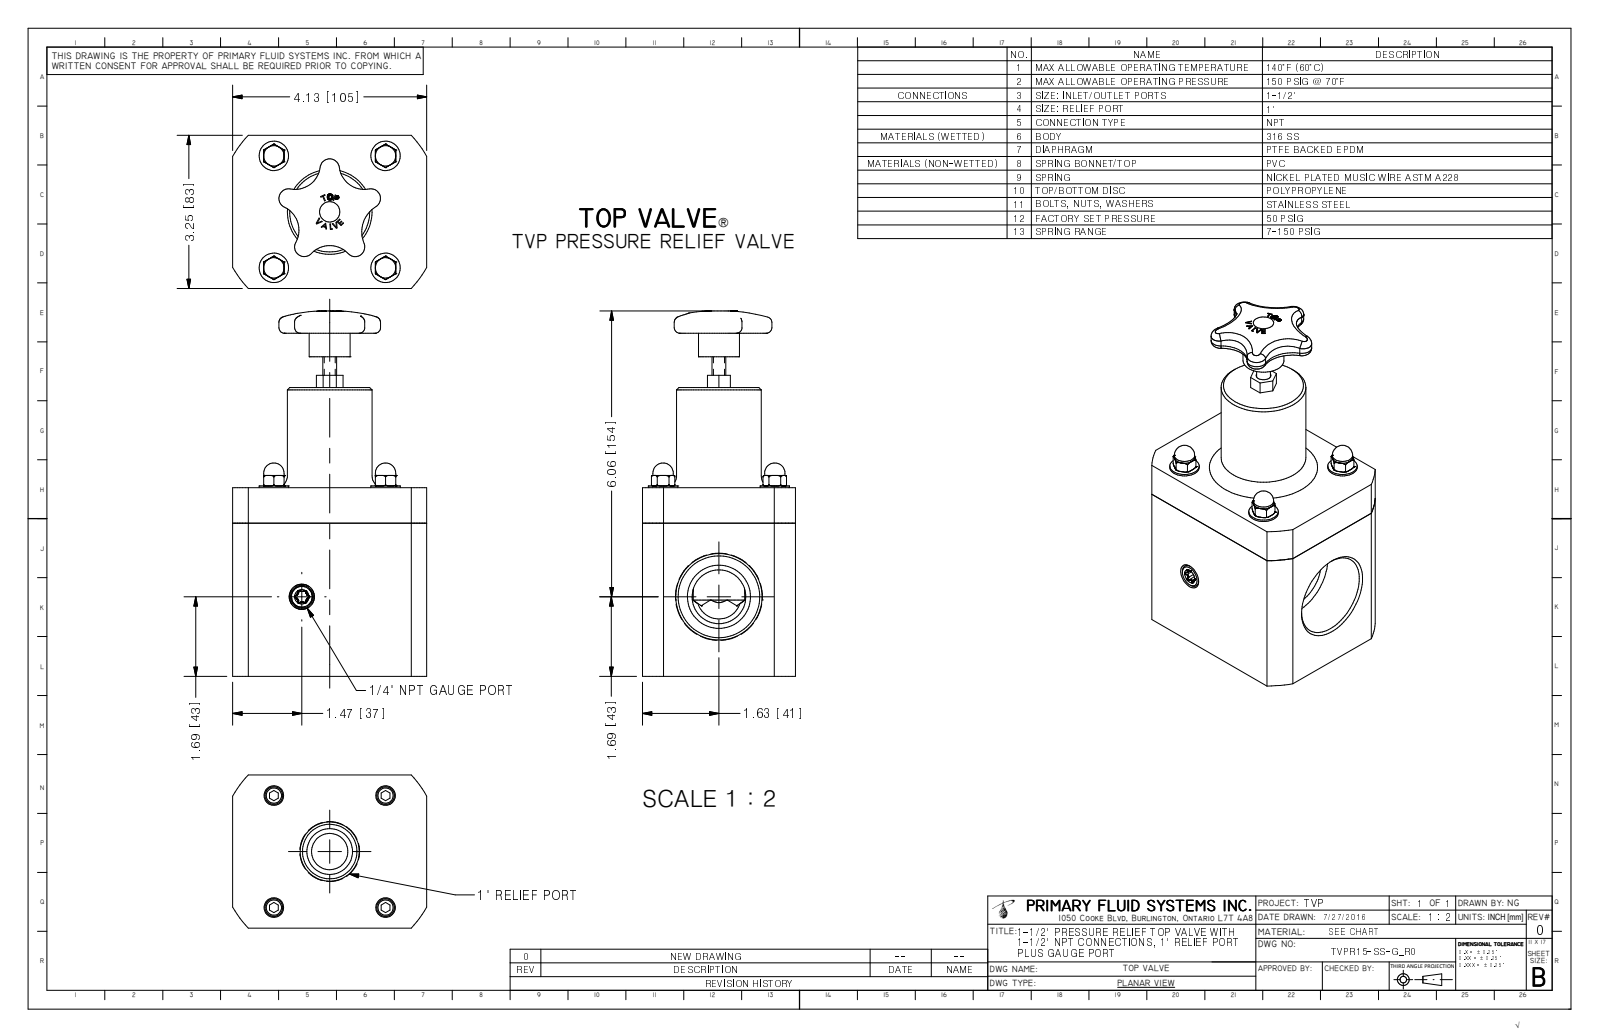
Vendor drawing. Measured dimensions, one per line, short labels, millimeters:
name: TVPR15-SS-G_R0
written by: Autodesk Inventor 2009 (AUTOMOTIVE_DESIGN)
unit: mm
bodies: 1 solid, 362 faces (153 planar, 52 cylindrical, 157 other)
size: 196.9 × 104.8 × 82.6
volume: 886 400 mm³; area: 78 770 mm²
holes: 4× ⌀4.4, 1× ⌀29.4, 1× ⌀44
bosses: 4× ⌀15.9, 4× ⌀11, 4× ⌀9.5, 1× ⌀45.7, 1× ⌀22.1, 1× ⌀7.4
rounds: 6× R0.7, 5× R2.2, 5× R5.2, 4× R13.6, 4× R16.7, 1× R15.9, 1× R18.9, 1× R60.3
face distances: 82.6, 101.6, 104.8, 25.4, 79.4, 54, 155.6, 15.2, 86.4, 140.3
hole spacings: 42.6, 42.7, 60.3, 60.3, 85.3
